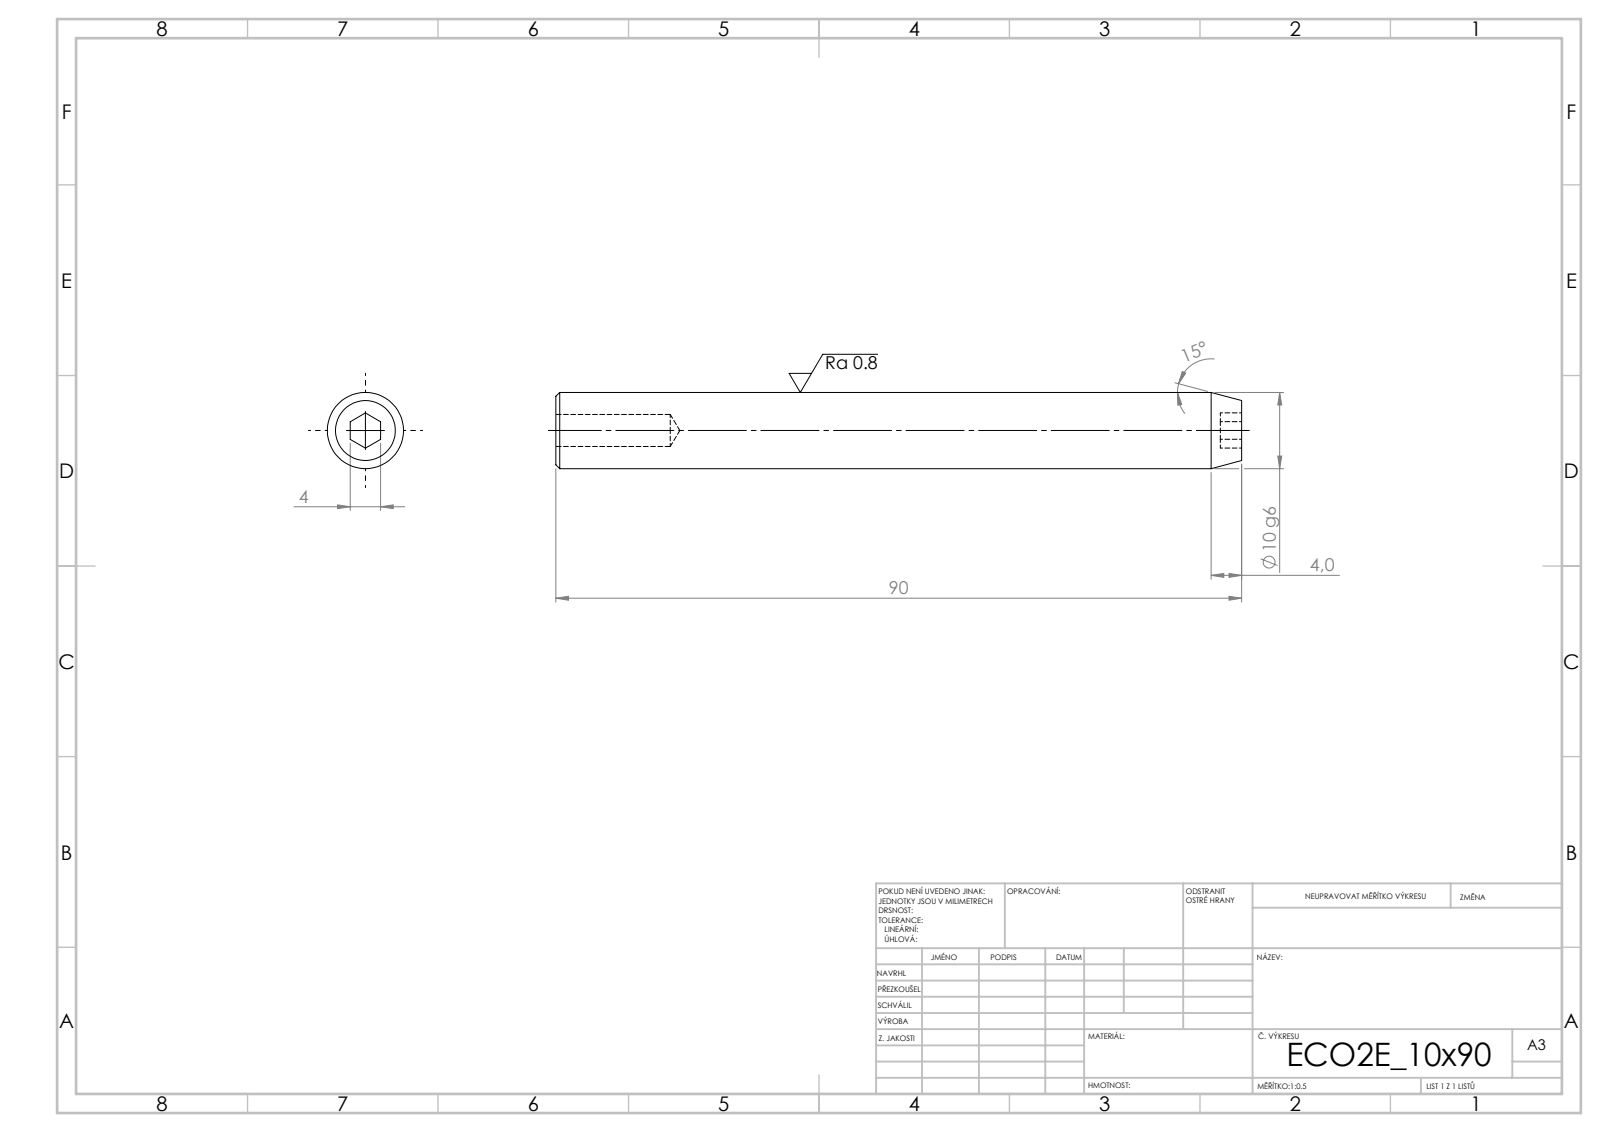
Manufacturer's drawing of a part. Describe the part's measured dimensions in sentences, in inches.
Its 3-D file was written by "SolidWorks 2019 (CONFIG_CONTROL_DESIGN)". It is 1 solid with 19 faces: 9 planar, 4 cylindrical and 6 other. Overall it measures 3.543 by 0.394 by 0.394 inches. Its volume is 0.412 cubic inches and its surface area 4.92 square inches. Round holes: 1 of diameter 0.165. Round bosses or shafts: 1 of diameter 0.394. The main face-to-face distances are 3.543, 0.157, 0.11, 3.433.
